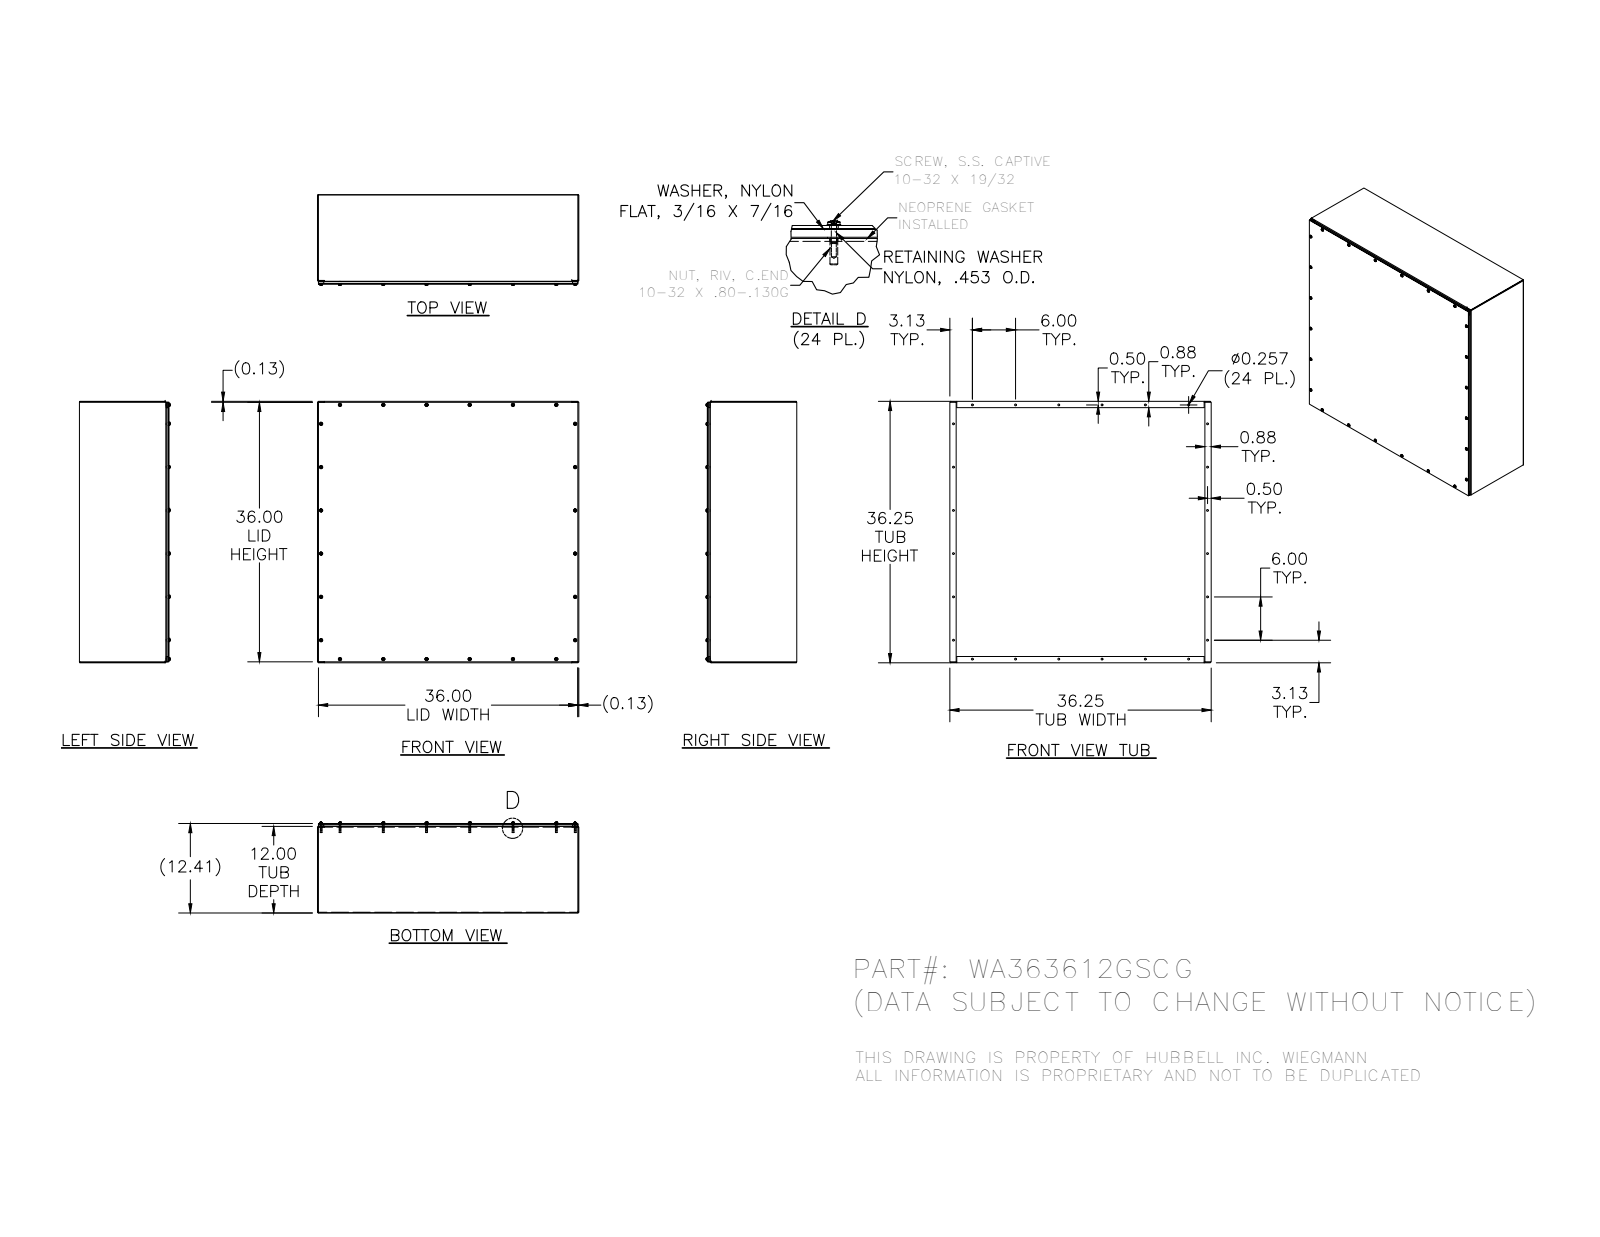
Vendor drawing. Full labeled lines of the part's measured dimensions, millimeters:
Part name (STEP PRODUCT): 34984; 39035; 37210; WA3636GSCGLP (+5 more)
STEP written by: SolidWorks 2014 (AUTOMOTIVE_DESIGN)
Units: millimetres
Bodies: 104 solids, 2408 faces (1124 planar, 636 cylindrical, 648 other)
Overall size (bounding box): 920.8 × 920.8 × 319.2
Volume: 7 266 000 mm³ · Surface area: 5 974 000 mm²
Round holes (diameter × count): ⌀4 ×24, ⌀4.8 ×24, ⌀5 ×24, ⌀6.5 ×24, ⌀7.1 ×24, ⌀7.1 ×24
Round bosses / shafts (diameter × count): ⌀11.5 ×24, ⌀11.1 ×24, ⌀10.3 ×24, ⌀6.3 ×24, ⌀4.2 ×24
Partial cylindrical surfaces — rounded edges, fillets, slot ends (radius × count): R2.3 ×24, R0.4 ×6, R2.8 ×6
Main face-to-face distances: 2.4, 312.9, 310.5, 315.3, 918.4, 920.8, 916, 2.4, 918.4, 916
Hole centre spacings: 152.4, 304.8, 457.2, 908.2, 945.8, 609.6, 895.4, 1005.3
